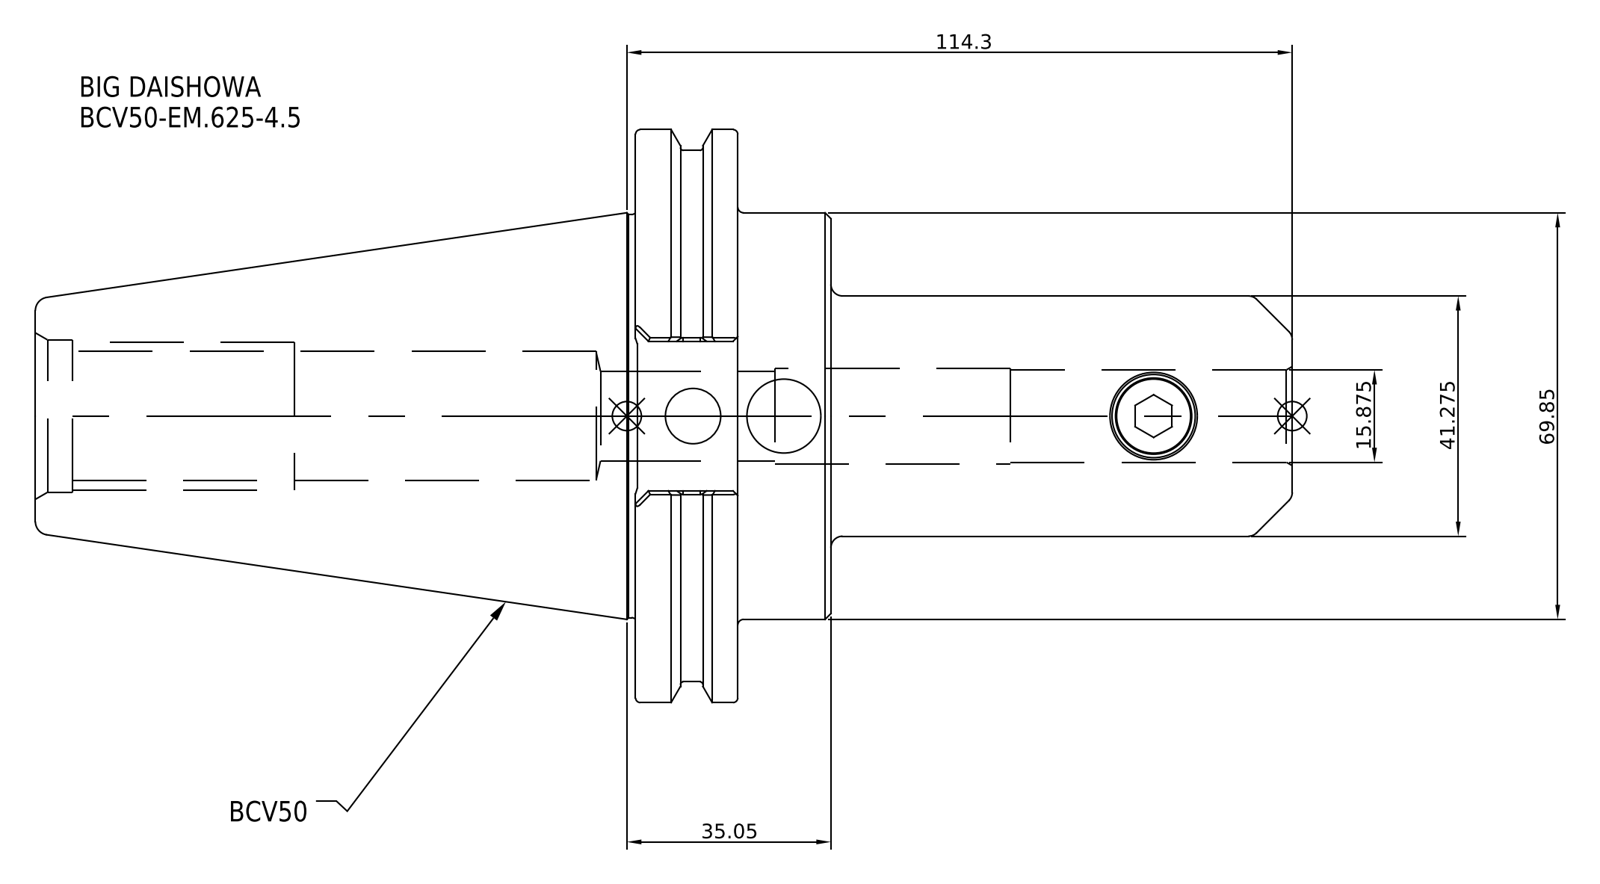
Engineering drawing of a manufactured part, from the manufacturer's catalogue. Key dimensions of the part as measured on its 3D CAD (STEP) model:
Part name (STEP PRODUCT): BCV50-EM_625-4_5
STEP written by: SolidWorks 2021 (CONFIG_CONTROL_DESIGN)
Units: millimetres
Bodies: 1 solid, 30 faces (8 planar, 14 cylindrical, 8 other)
Overall size (bounding box): 215.9 × 98.43 × 98.43
Volume: 530 546 mm³ · Surface area: 54 653 mm²
Round holes (diameter × count): ⌀15.88 ×1
Round bosses / shafts (diameter × count): ⌀98.43 ×1, ⌀91.29 ×1, ⌀69.85 ×1, ⌀41.3 ×1
Main face-to-face distances: 17.55, 16, 33.55, 136.65, 120.65, 103.1, 79.25, 95.25, 112.8, 215.9
